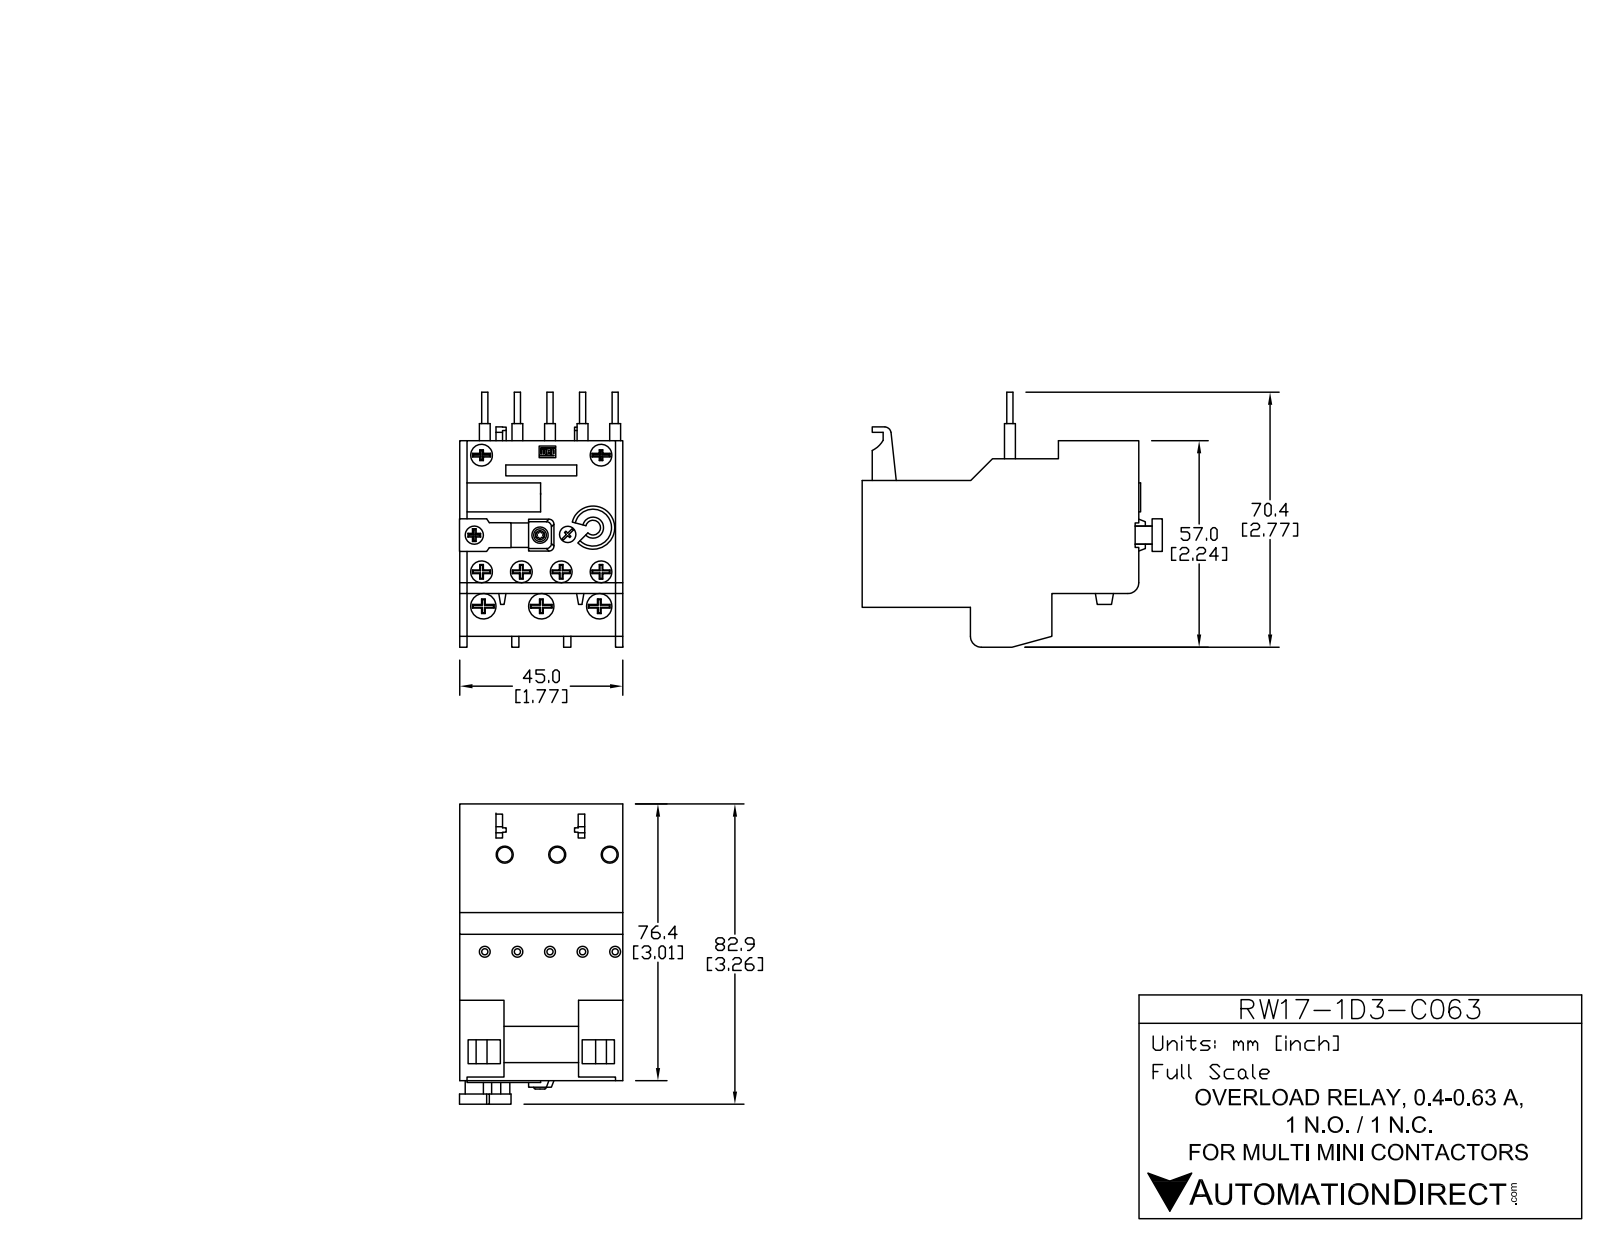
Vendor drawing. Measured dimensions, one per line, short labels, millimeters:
name: RW17D-1D3-C063
written by: SolidWorks 2013 (AUTOMOTIVE_DESIGN)
unit: mm
bodies: 18 solids, 756 faces (515 planar, 214 cylindrical, 27 other)
size: 82.65 × 70.5 × 45.55
volume: 127 454 mm³; area: 34 704 mm²
holes: 6× ⌀6, 3× ⌀4, 3× ⌀7, 3× ⌀7.5, 1× ⌀4.5, 1× ⌀4.75, 1× ⌀5.33, 1× ⌀5.5, 1× ⌀10.42
bosses: 7× ⌀5.5, 7× ⌀3, 5× ⌀1.75, 2× ⌀5.6, 2× ⌀3.25, 1× ⌀6.42, 1× ⌀6.15, 1× ⌀4.75
rounds: 20× R0.5, 12× R0.25, 9× R1, 6× R4.52, 4× R5.86, 4× R7.86, 3× R1.5, 2× R1.25
face distances: 45.5, 1.5, 10.85, 11, 76.4, 35, 1.42, 74.98, 74.9, 6
hole spacings: 15, 8.55, 10.75, 30, 10.57, 11.86, 14.25, 21.35
